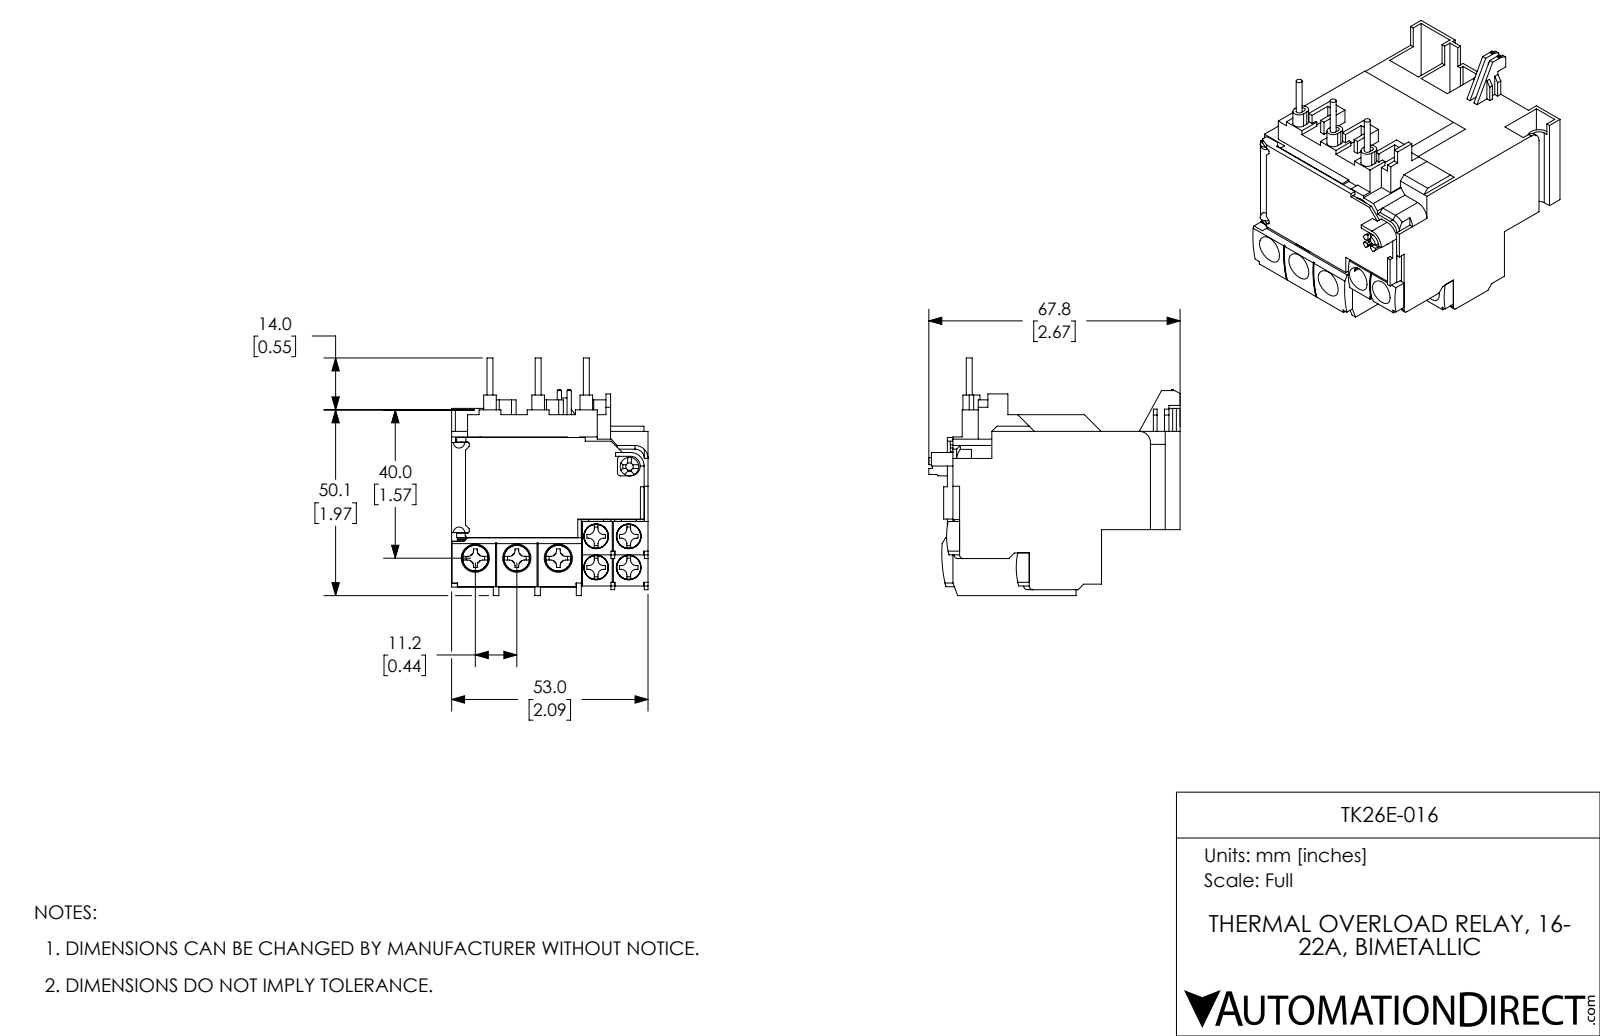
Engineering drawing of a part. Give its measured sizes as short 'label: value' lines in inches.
name: TK26E-016
written by: SolidWorks 2017 (AUTOMOTIVE_DESIGN)
unit: in
bodies: 38 solids, 1480 faces (1225 planar, 220 cylindrical, 35 other)
size: 2.669 × 2.524 × 2.087
volume: 6.099 in³; area: 60.15 in²
holes: 4× ⌀0.138, 4× ⌀0.142, 4× ⌀0.264, 3× ⌀0.157, 3× ⌀0.161, 3× ⌀0.299, 1× ⌀0.039, 1× ⌀0.079, 1× ⌀0.197, 1× ⌀0.433
bosses: 4× ⌀0.26, 3× ⌀0.063, 1× ⌀0.236
rounds: 28× R0.059, 8× R0.039, 6× R0.02, 6× R0.067, 5× R0.031, 4× R0.047, 4× R0.171, 3× R0.189
face distances: 0.039, 0.354, 0.059, 0.472, 2.087, 0.079, 0.394, 0.433, 0.343, 0.028
hole spacings: 0.331, 0.346, 0.441, 0.479, 0.376, 0.413, 0.464, 0.74
